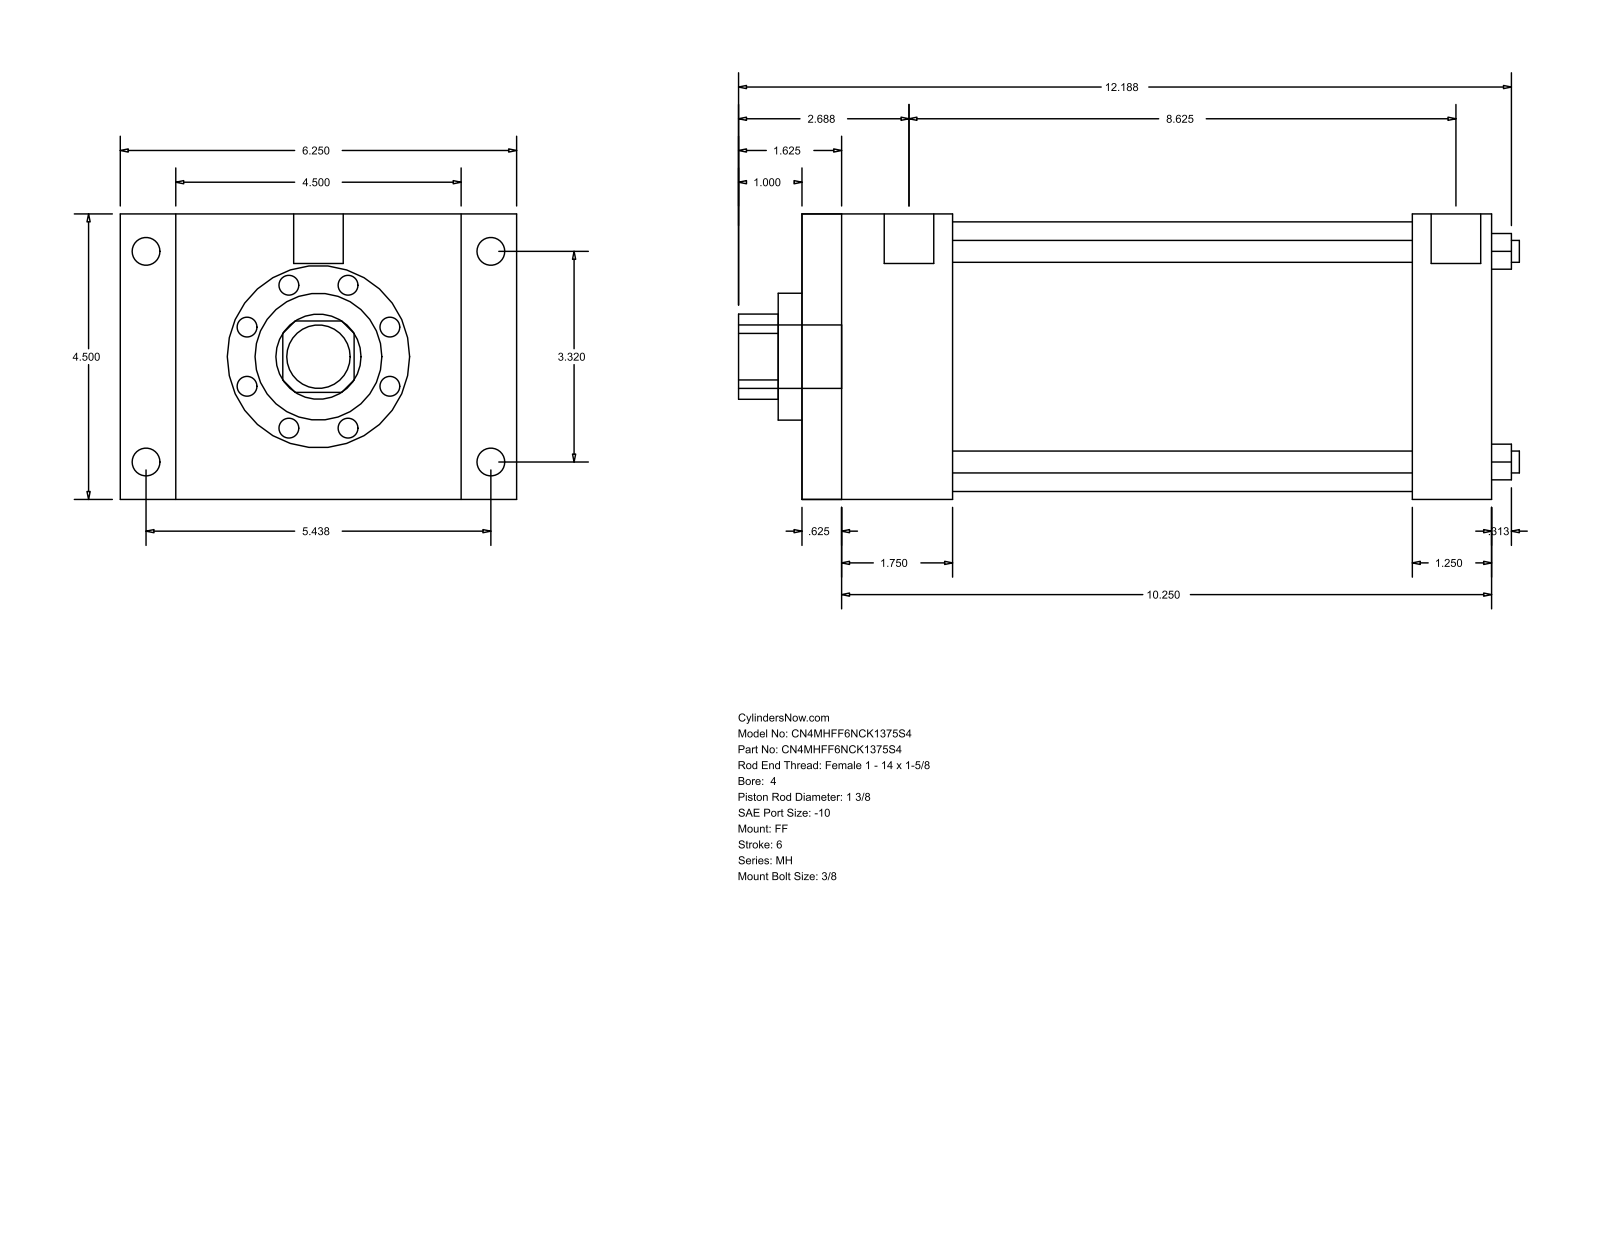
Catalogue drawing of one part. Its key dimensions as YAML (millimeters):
part_name: "MH_FF__0400_1.375"
step_written_by: "GSSL Pune (CONFIG_CONTROL_DESIGN)"
units: millimeters
bodies: {solids: 0, faces: 92, planar: 64, cylindrical: 28, other: 0}
overall_size: [312.74, 158.75, 114.3]
round_holes:
  - {diameter: 8.76, count: 4}
  - {diameter: 34.92, count: 1}
  - {diameter: 50.8, count: 1}
  - {diameter: 107.95, count: 1}
round_bosses_or_shafts:
  - {diameter: 11.13, count: 4}
  - {diameter: 8.73, count: 4}
  - {diameter: 19.84, count: 2}
  - {diameter: 25.4, count: 1}
partial_cylinders:
  - {radius: 17.06, count: 1}
face_to_face_distances: [114.3, 276.22, 15.87, 260.35, 60.32, 44.45, 215.9, 244.48, 228.61, 184.16]
hole_center_spacings: [59.62, 84.32, 119.25]
